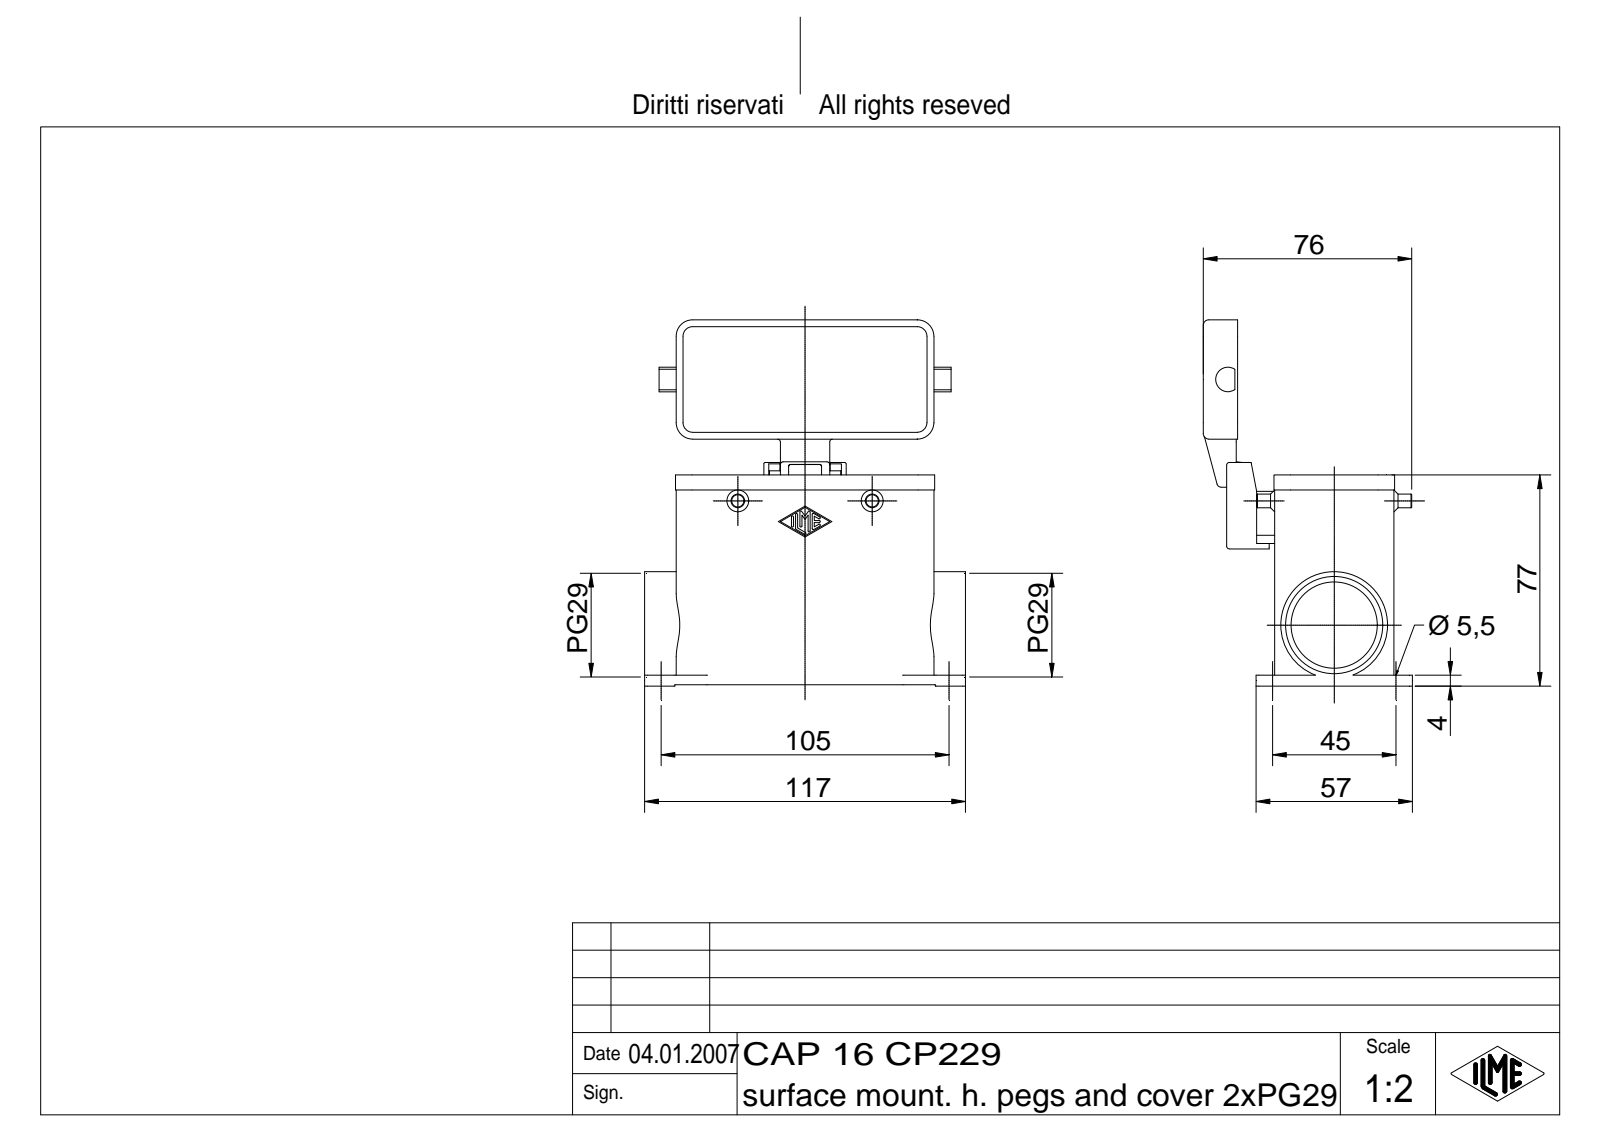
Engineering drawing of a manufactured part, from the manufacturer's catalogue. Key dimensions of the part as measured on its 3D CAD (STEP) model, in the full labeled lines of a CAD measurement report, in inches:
Part name (STEP PRODUCT): CAP 16 CP229
STEP written by: Autodesk Inventor 7 (AUTOMOTIVE_DESIGN)
Units: inches
Bodies: 2 solids, 474 faces (175 planar, 179 cylindrical, 120 other)
Overall size (bounding box): 5.256 × 4.606 × 3.002
Volume: 7.66 in³ · Surface area: 113.7 in²
Round holes (diameter × count): ⌀0.217 ×4, ⌀0.157 ×1, ⌀0.197 ×1, ⌀1.239 ×1, ⌀1.397 ×1
Round bosses / shafts (diameter × count): ⌀0.197 ×2, ⌀0.118 ×2, ⌀1.535 ×1, ⌀0.276 ×1, ⌀0.157 ×1
Partial cylindrical surfaces — rounded edges, fillets, slot ends (radius × count): R0.039 ×26, R0.015 ×14, R0.236 ×12, R0.02 ×9, R0.028 ×8, R0.079 ×8, R0.118 ×4, R0.138 ×4
Main face-to-face distances: 0.118, 1.594, 0.138, 1.713, 1.476, 1.142, 0.886, 2.736, 2.618, 1.024
Hole centre spacings: 1.772, 4.134, 4.498
